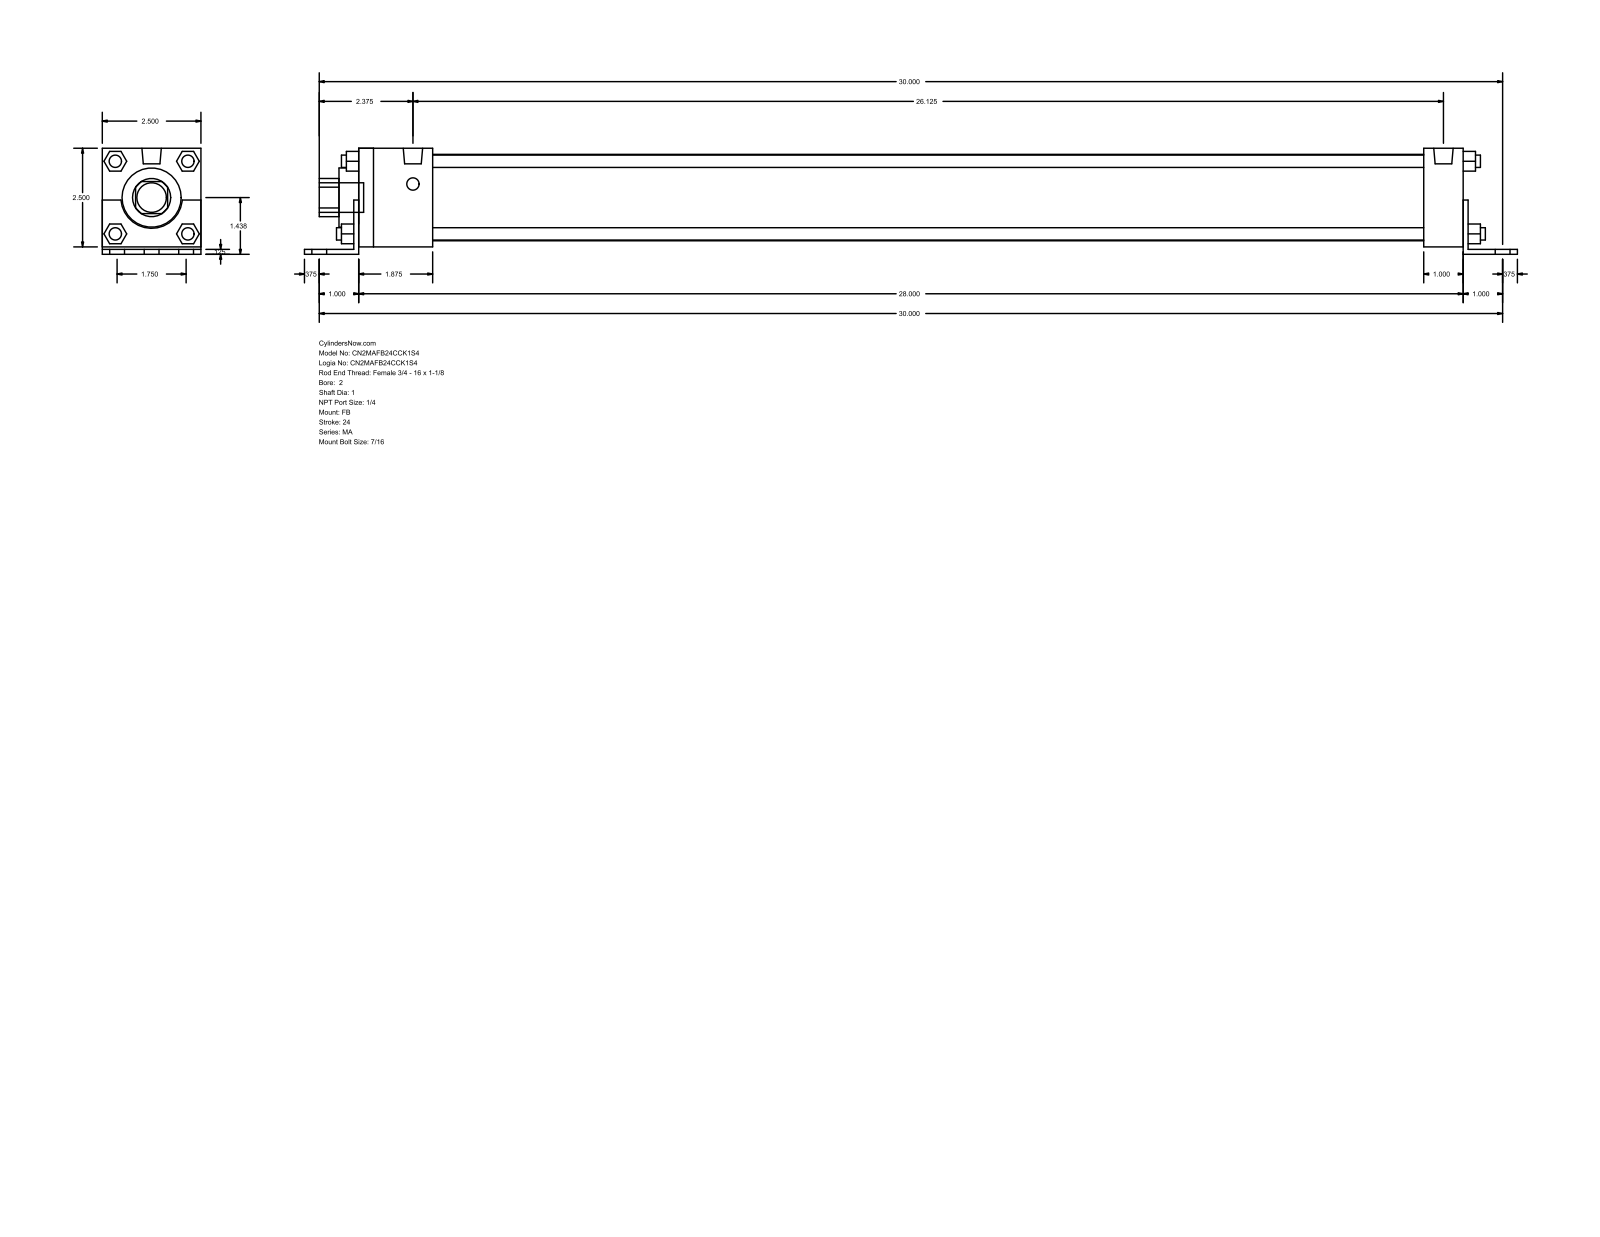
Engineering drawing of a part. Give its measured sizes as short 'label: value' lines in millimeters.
name: MA_FB__0200_1
written by: GSSL Pune (CONFIG_CONTROL_DESIGN)
unit: mm
bodies: 0 solids, 140 faces (105 planar, 35 cylindrical, 0 other)
size: 781.05 × 68.26 × 63.5
holes: 1× ⌀25.4, 1× ⌀38.1, 1× ⌀55.63
bosses: 8× ⌀7.94, 6× ⌀11.11, 2× ⌀12.49, 1× ⌀19.05
rounds: 1× R12.29, 1× R19.81
face distances: 63.5, 3.17, 4.76, 68.26, 1.59, 65.09, 714.37, 12.7, 711.2, 25.4
